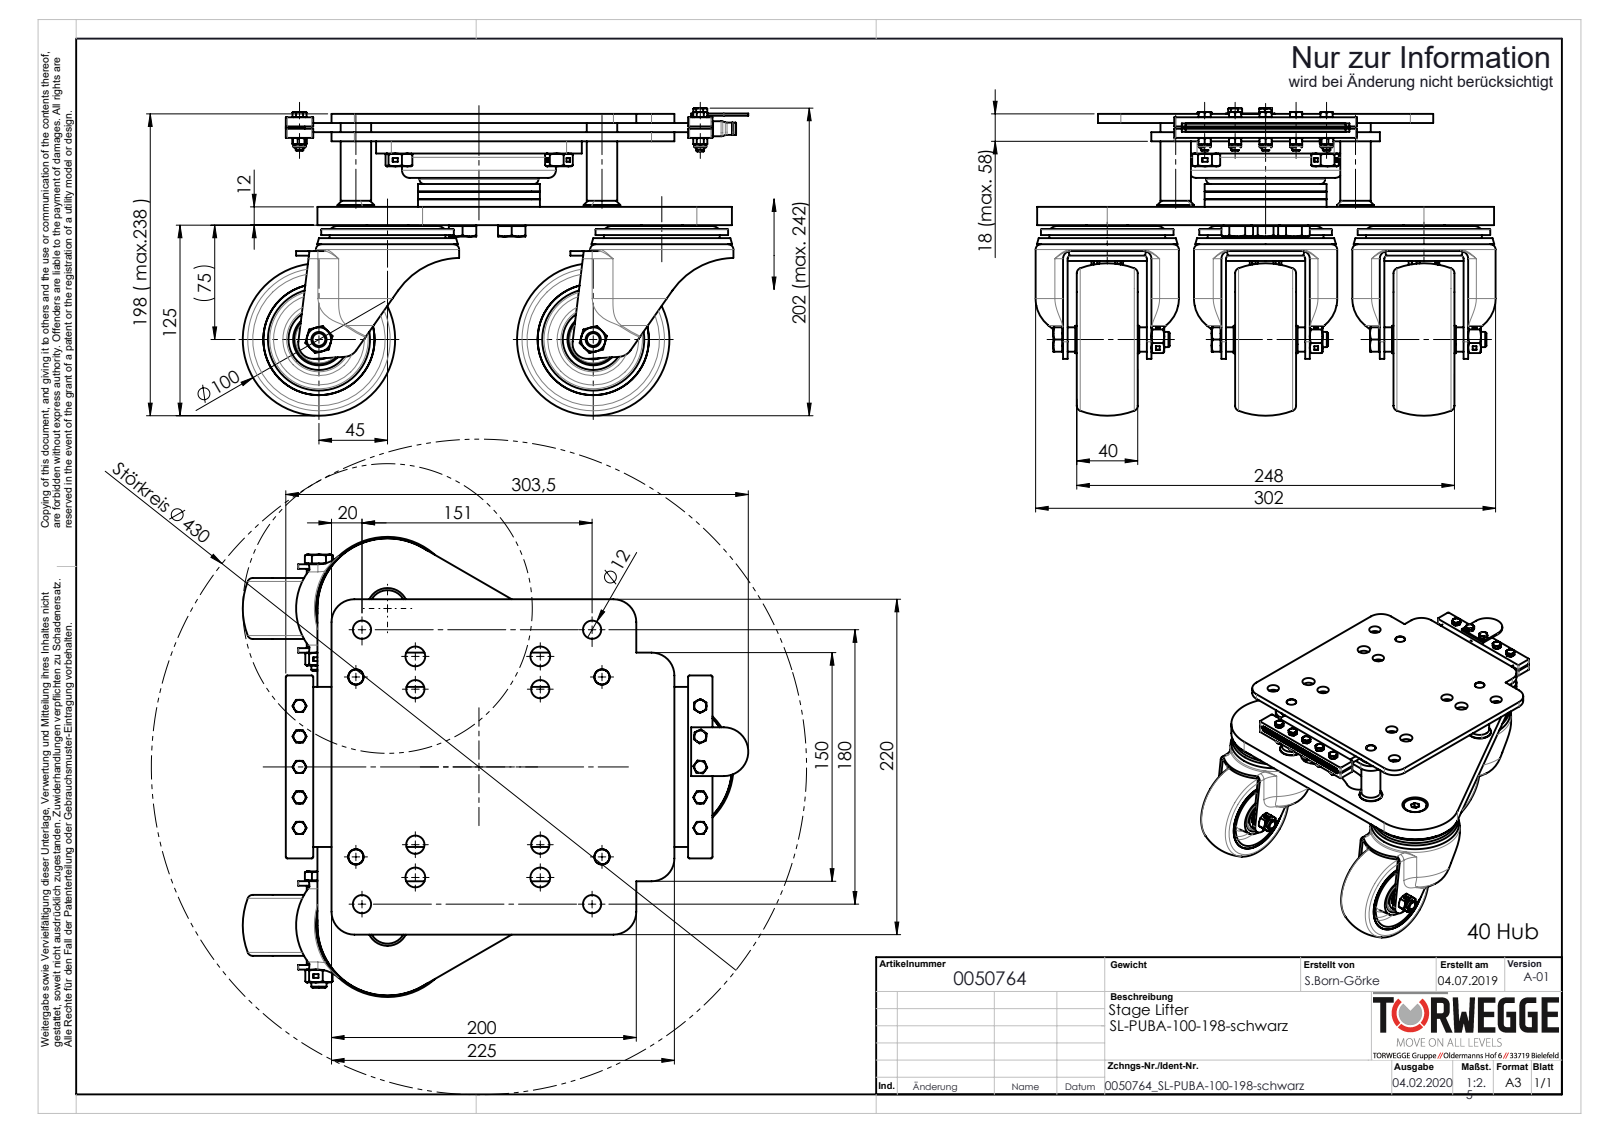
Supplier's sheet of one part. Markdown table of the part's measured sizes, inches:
| quantity | value |
| --- | --- |
| part name | 0050764_SL-PUBA-100-198-schwarz_(A-01) |
| STEP written by | SolidWorks 2018 (AUTOMOTIVE_DESIGN) |
| units | inches |
| bodies | 132 solids, 2895 faces (1042 planar, 820 cylindrical, 1033 other) |
| overall size | 13.061 × 11.884 × 7.943 |
| volume | 172.3 in³ |
| surface area | 1 397 in² |
| round holes (diameter × count) | 0.472 × 19, 0.163 × 10, 0.197 × 10, 0.226 × 10, 0.402 × 10, 0.492 × 7, 0.512 × 7, 0.335 × 6, 0.394 × 6, 0.866 × 4, 0.236 × 3, 0.5 × 3 |
| round bosses / shafts (diameter × count) | 0.202 × 16, 0.315 × 10, 0.787 × 8, 0.945 × 7, 0.709 × 5, 0.472 × 5, 0.387 × 4, 3.701 × 3 |
| partial cylindrical surfaces (radius × count) | 0.197 × 9, 0.039 × 8, 0.217 × 8, 0.394 × 8, 0.591 × 8, 0.079 × 6, 3.375 × 4, 1.616 × 3 |
| main face-to-face distances | 0.236, 0.472, 2.165, 2.402, 1.929, 2.638, 0.709, 1.693, 2.874, 0.197 |
| hole center spacings | 5.2, 0.846, 1.363, 3.228, 3.337, 4.015, 4.862, 5.305 |
